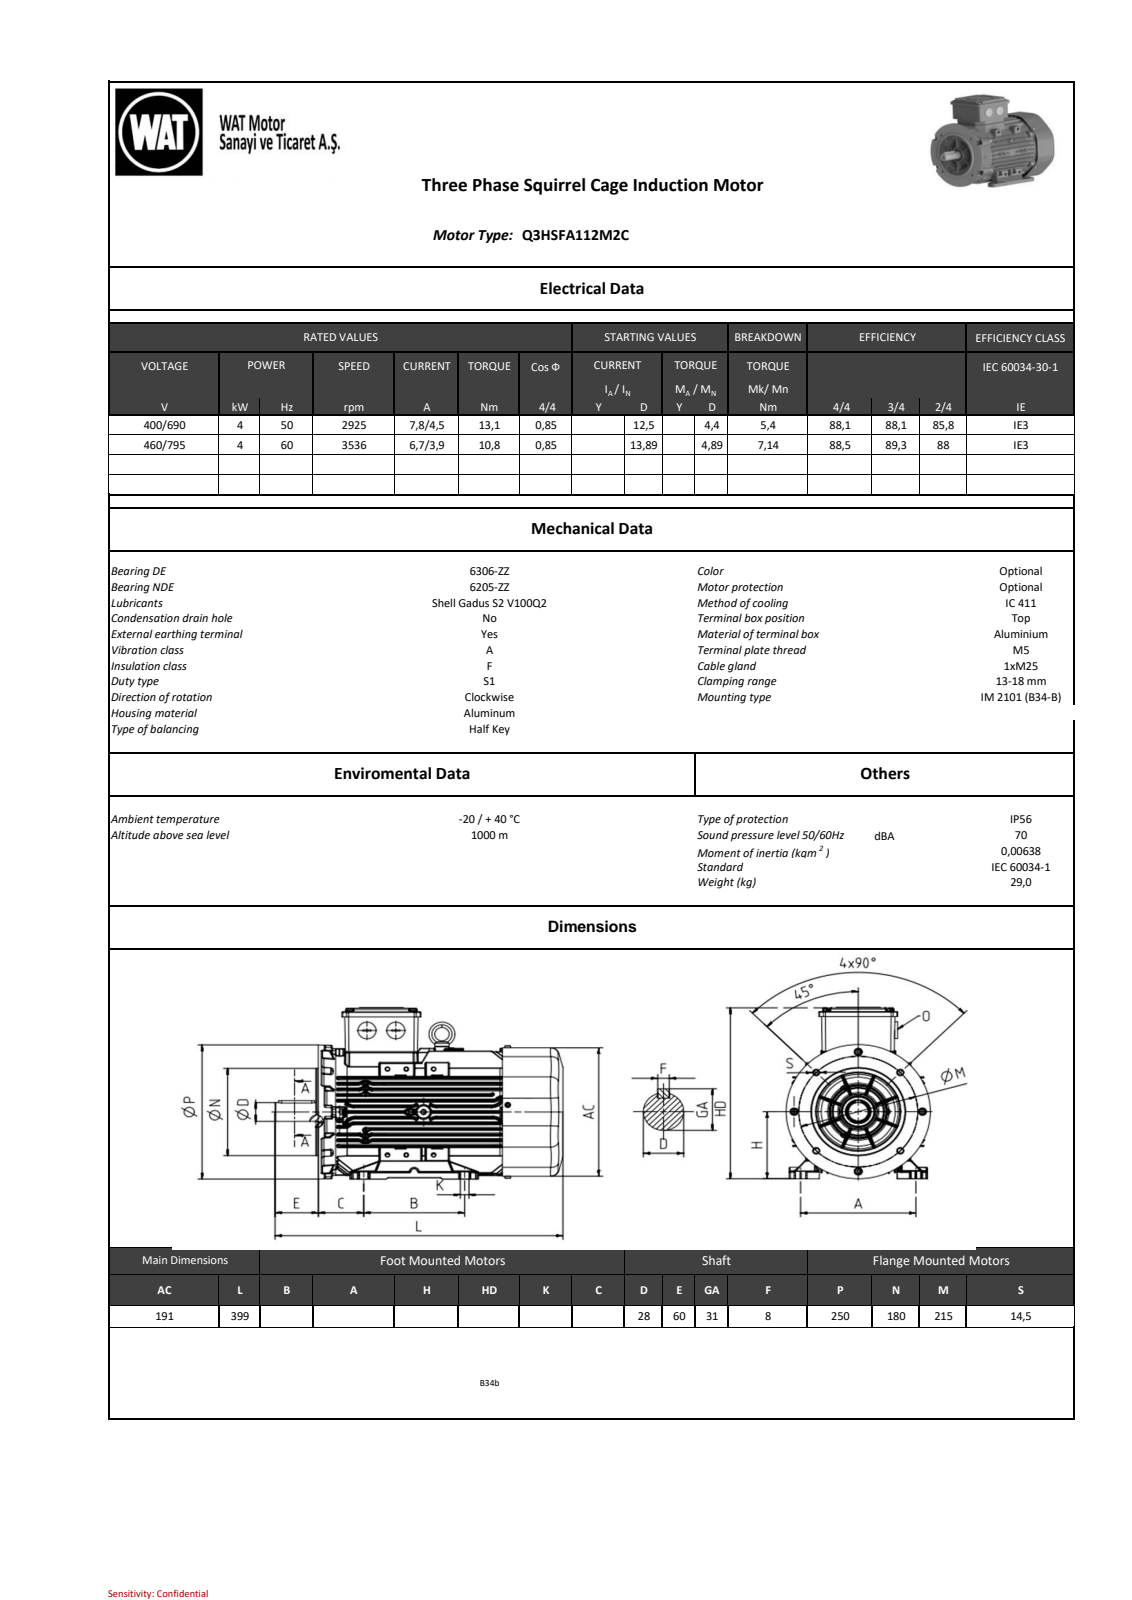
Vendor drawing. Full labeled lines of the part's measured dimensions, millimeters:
Part name (STEP PRODUCT): QHS Series_ 112_B5_stp_objects
STEP written by: SIEMENS PLM Software NX2206.8101 (AUTOMOTIVE_DESIGN)
Units: millimetres
Bodies: 0 solids, 5871 faces (1215 planar, 2219 cylindrical, 2437 other)
Overall size (bounding box): 399.31 × 268.18 × 249.93
Round holes (diameter × count): ⌀10 ×1, ⌀44.42 ×1, ⌀57.4 ×1, ⌀89 ×1, ⌀109 ×1, ⌀129 ×1, ⌀133 ×1
Round bosses / shafts (diameter × count): ⌀8 ×8, ⌀8.5 ×4, ⌀5 ×4, ⌀25 ×3, ⌀180 ×1, ⌀113.5 ×1, ⌀93.5 ×1, ⌀60.74 ×1
Partial cylindrical surfaces — rounded edges, fillets, slot ends (radius × count): R1 ×639, R0.8 ×545, R0.5 ×76, R2 ×61, R2.5 ×61, R0.81 ×48, R5 ×40, R15 ×26
Main face-to-face distances: 8.53, 8.46, 8.45, 76.24, 16.91, 93.45, 25.58, 17.05, 76.68, 59.63
